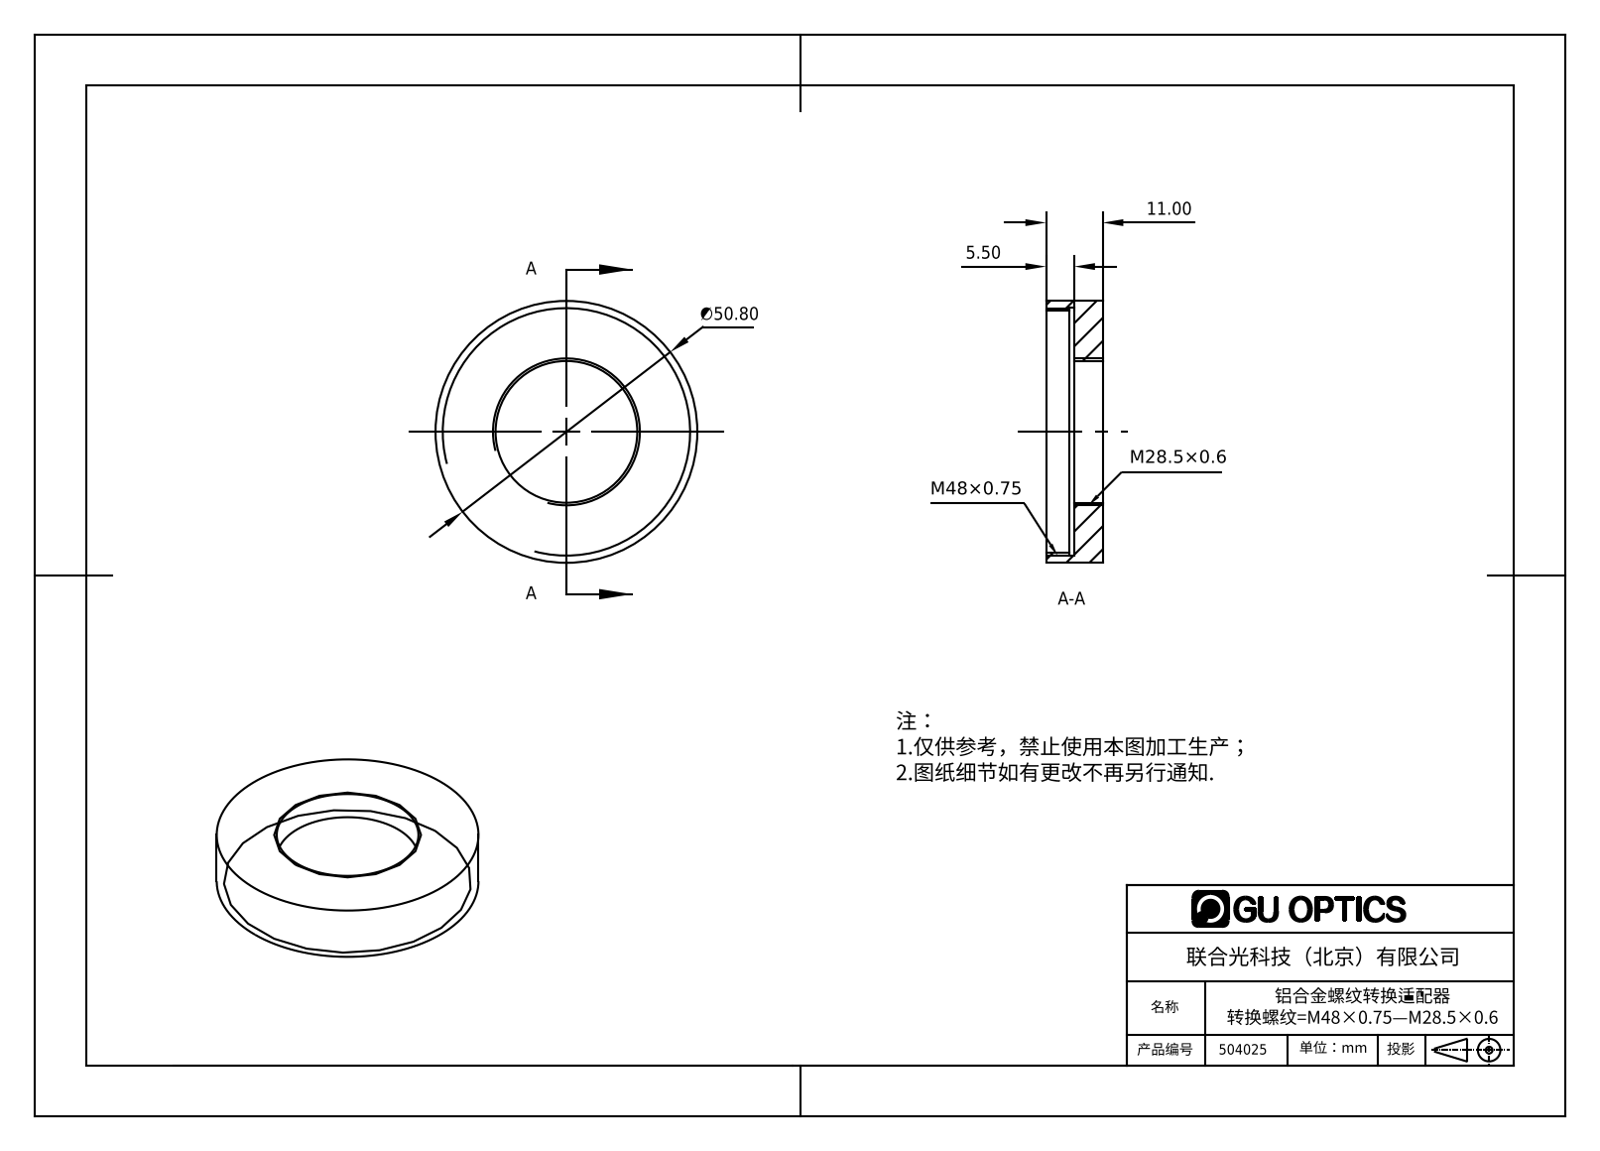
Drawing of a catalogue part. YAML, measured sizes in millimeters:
part_name: "504025"
step_written_by: "SolidWorks 2016 (AUTOMOTIVE_DESIGN)"
units: millimeters
bodies: {solids: 1, faces: 12, planar: 4, cylindrical: 8, other: 0}
overall_size: [50.8, 50.8, 11]
volume: 9396
surface_area: 6092
round_holes:
  - {diameter: 27.5, count: 1}
  - {diameter: 47, count: 1}
  - {diameter: 48.2, count: 1}
round_bosses_or_shafts:
  - {diameter: 50.8, count: 1}
face_to_face_distances: [5.5, 11, 4.5, 1, 6.5]
